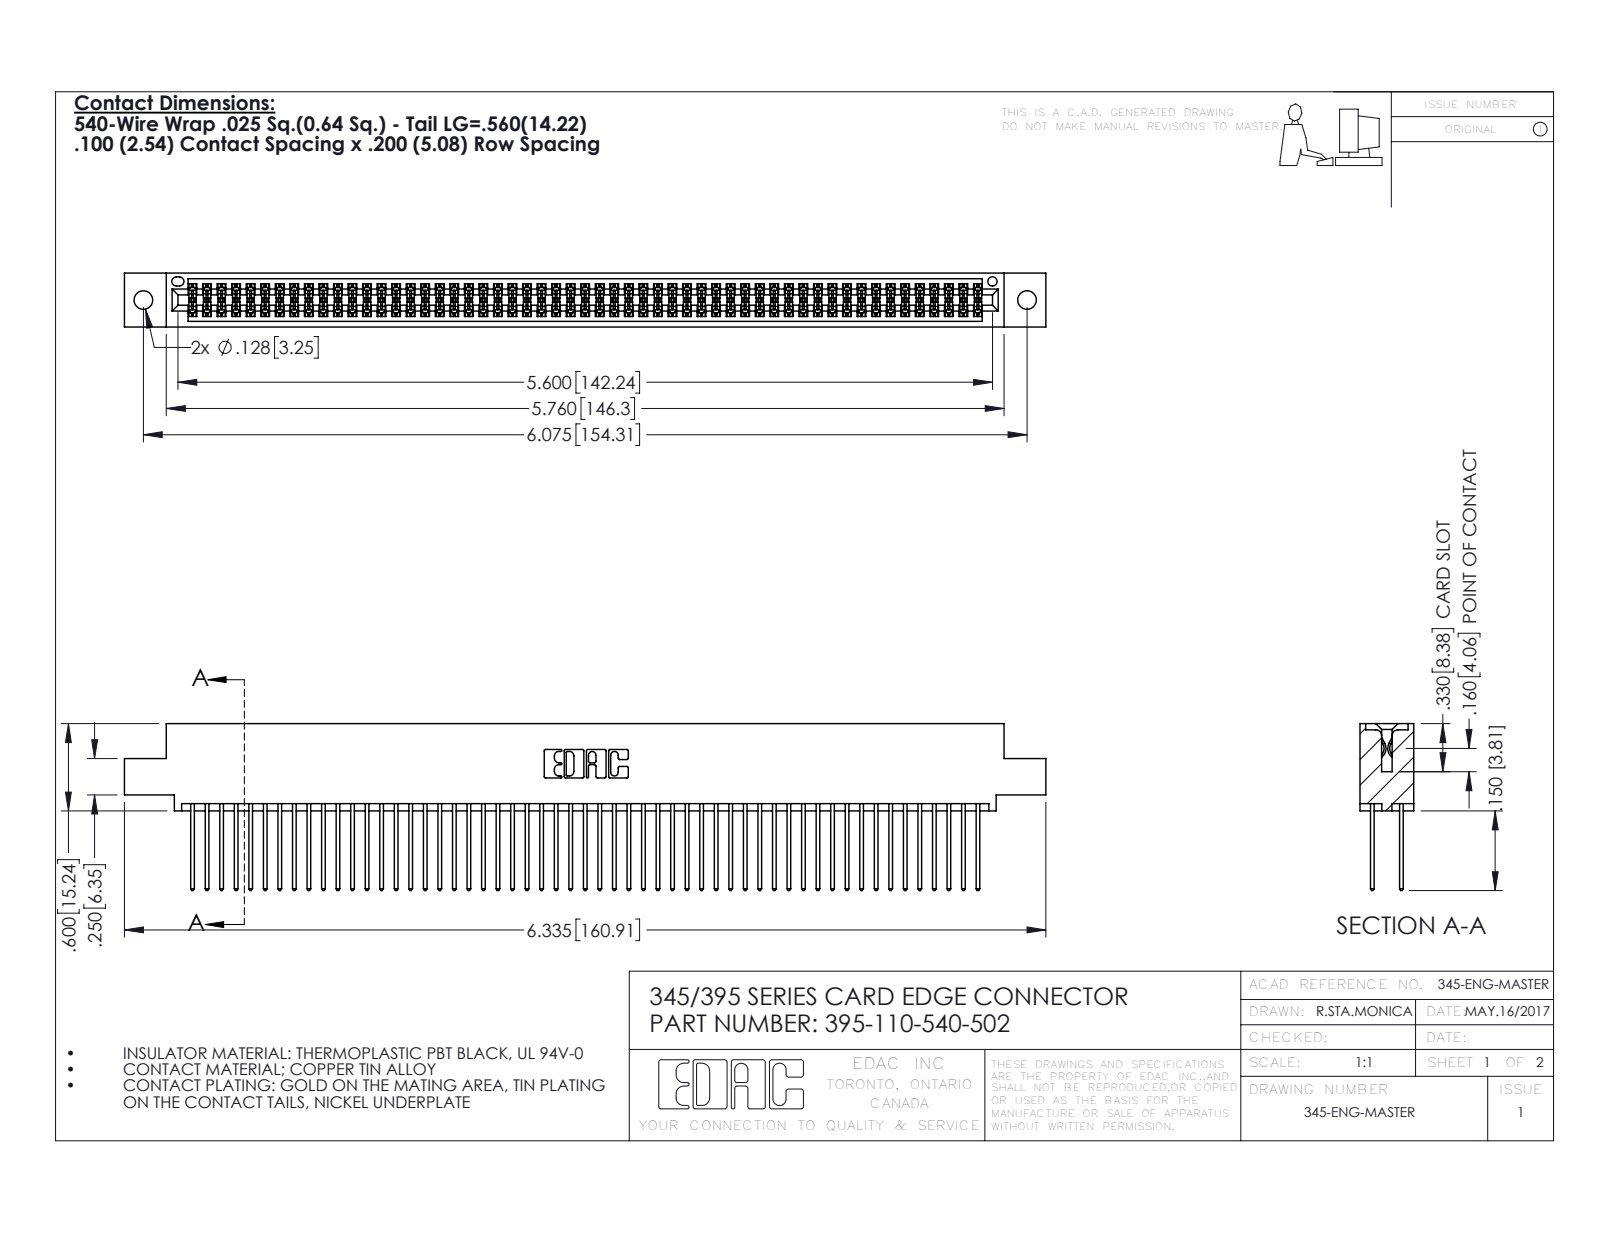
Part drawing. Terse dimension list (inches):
name: 345-292-001_345-293-140; 345 Part_0.110 Offset - 0.128 Dia; 395-110-540-502
written by: SolidWorks 2016 (CONFIG_CONTROL_DESIGN)
unit: in
bodies: 111 solids, 5630 faces (3714 planar, 1916 cylindrical, 0 other)
size: 6.335 × 1.147 × 0.37
volume: 0.98 in³; area: 39.9 in²
holes: 2× ⌀0.128, 1× ⌀0.064
rounds: 165× R0.006, 110× R0.01, 22× R0.01, 6× R0.007, 6× R0.031, 3× R0.026, 2× R0.014, 2× R0.019
face distances: 0.072, 0.298, 0.2, 0.098, 0.272, 0.025, 0.37, 0.225, 0.175, 0.149
hole spacings: 0.27, 5.839, 6.075
